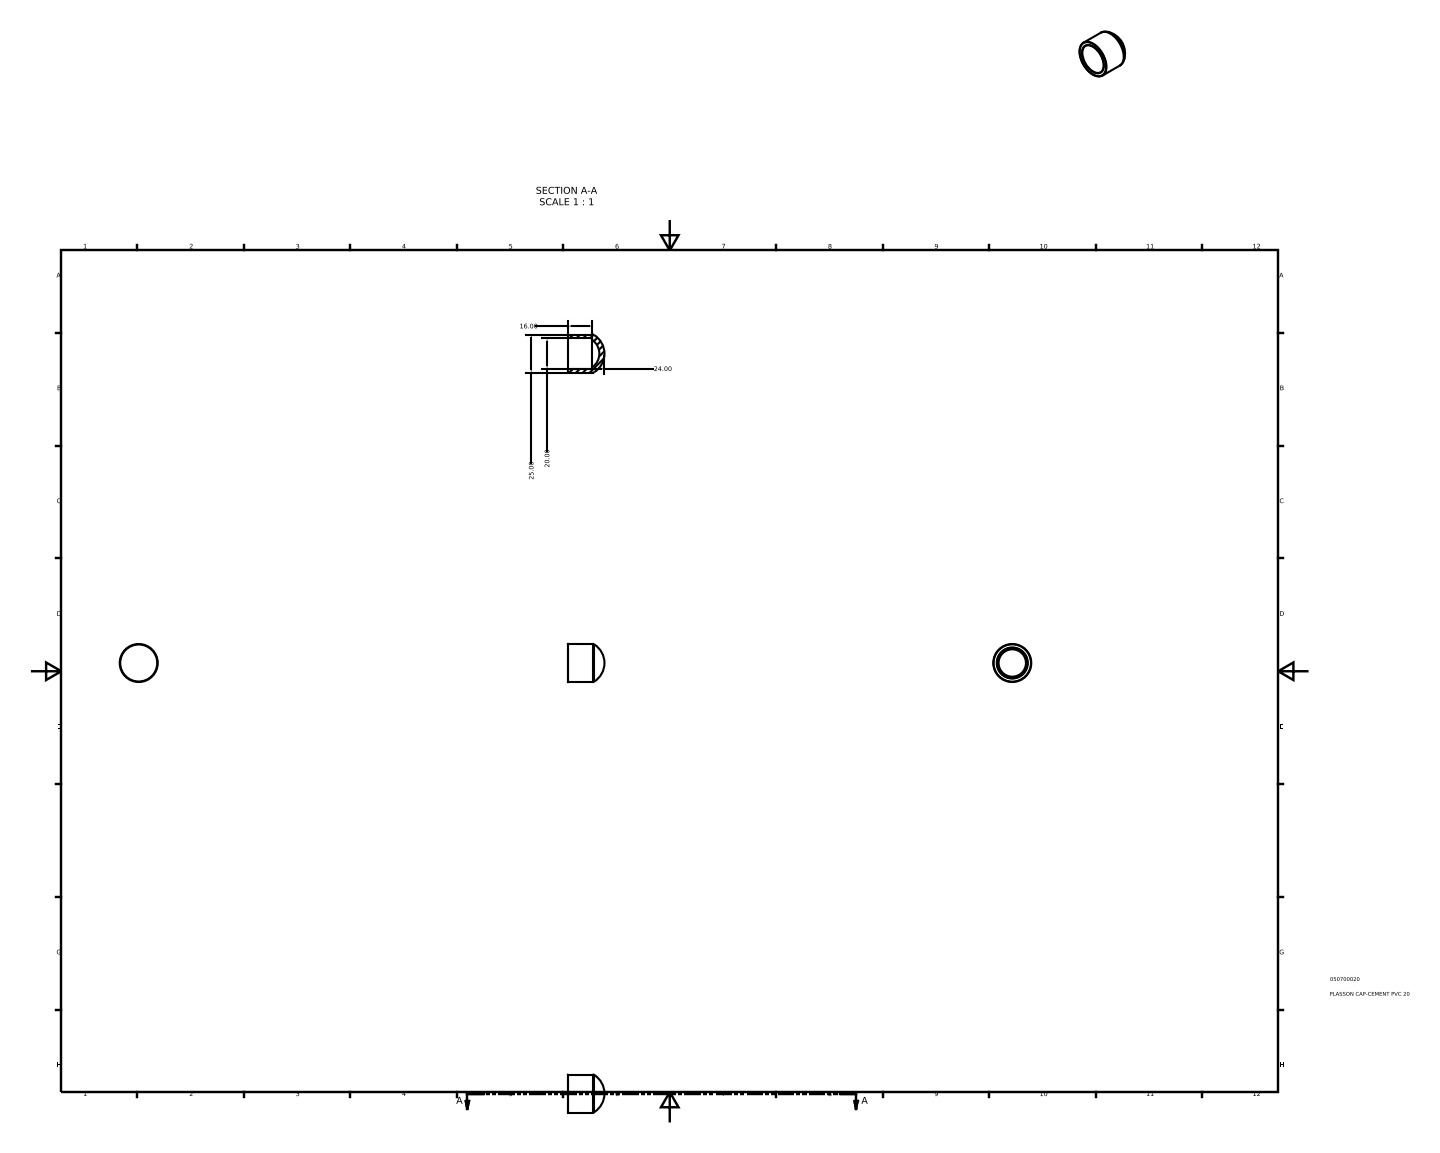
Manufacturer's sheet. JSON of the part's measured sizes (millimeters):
{"part_name": "050700020", "step_written_by": "Autodesk Inventor 2015 (AUTOMOTIVE_DESIGN)", "units": "millimeters", "bodies": {"solids": 1, "faces": 9, "planar": 2, "cylindrical": 2, "other": 5}, "overall_size": [25, 25, 24], "volume_mm3": 4539, "surface_area_mm2": 3522, "round_holes": [[20, 1]], "round_bosses_or_shafts": [[25, 1]], "face_to_face_distances": [16]}
